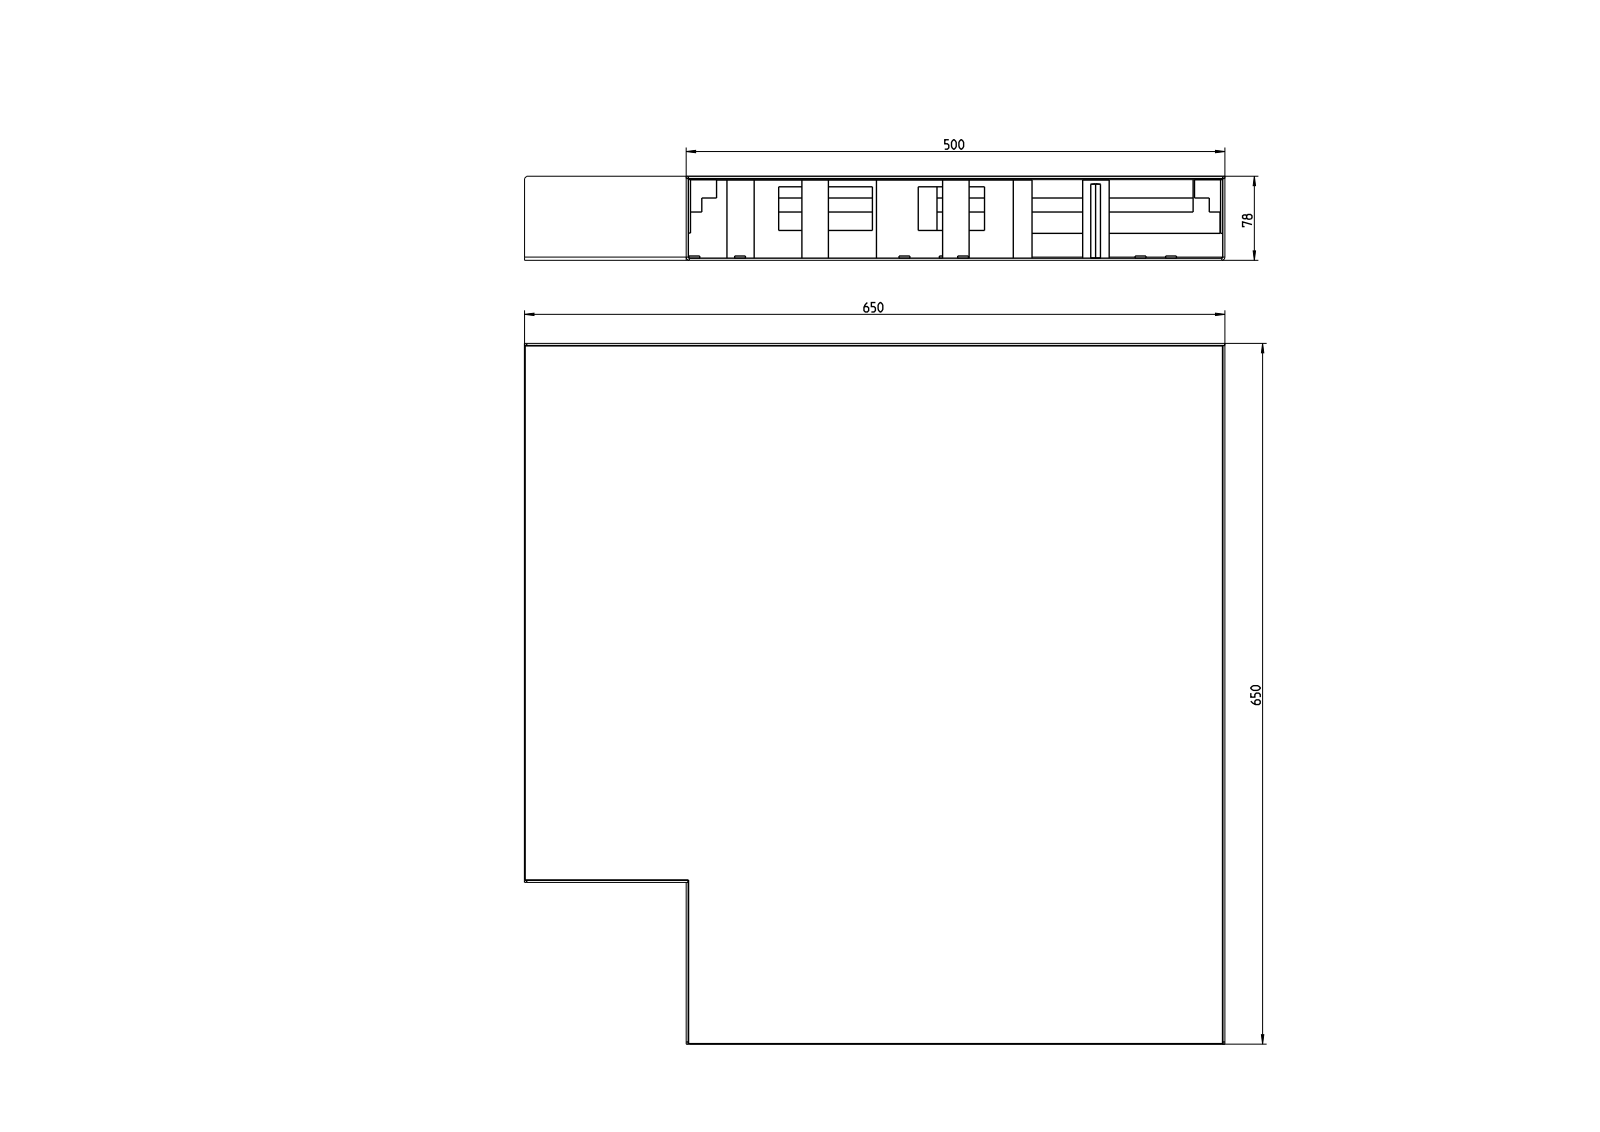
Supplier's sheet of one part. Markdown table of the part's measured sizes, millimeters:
| quantity | value |
| --- | --- |
| part name | T-01229; T-01222; T-01248; T-01247 (+8 more) |
| STEP written by | CREO PARAMETRIC BY PTC INC, 2022024 (AUTOMOTIVE_DESIGN) |
| units | millimeters |
| bodies | 18 solids, 498 faces (341 planar, 105 cylindrical, 52 other) |
| overall size | 813.76 × 755.09 × 78.23 |
| volume | 4 516 000 mm³ |
| surface area | 2 610 000 mm² |
| round holes (diameter × count) | 6 × 12, 6.5 × 8, 13.6 × 7 |
| round bosses / shafts (diameter × count) | 10 × 12 |
| partial cylindrical surfaces (radius × count) | 0.1 × 4, 1 × 4, 3 × 4 |
| main face-to-face distances | 2, 72.8, 1, 73.8, 74.8, 75.8, 4, 130, 496, 24.6 |
| hole center spacings | 20, 400, 97.57, 400.5, 411.73, 33, 53, 75.48 |
